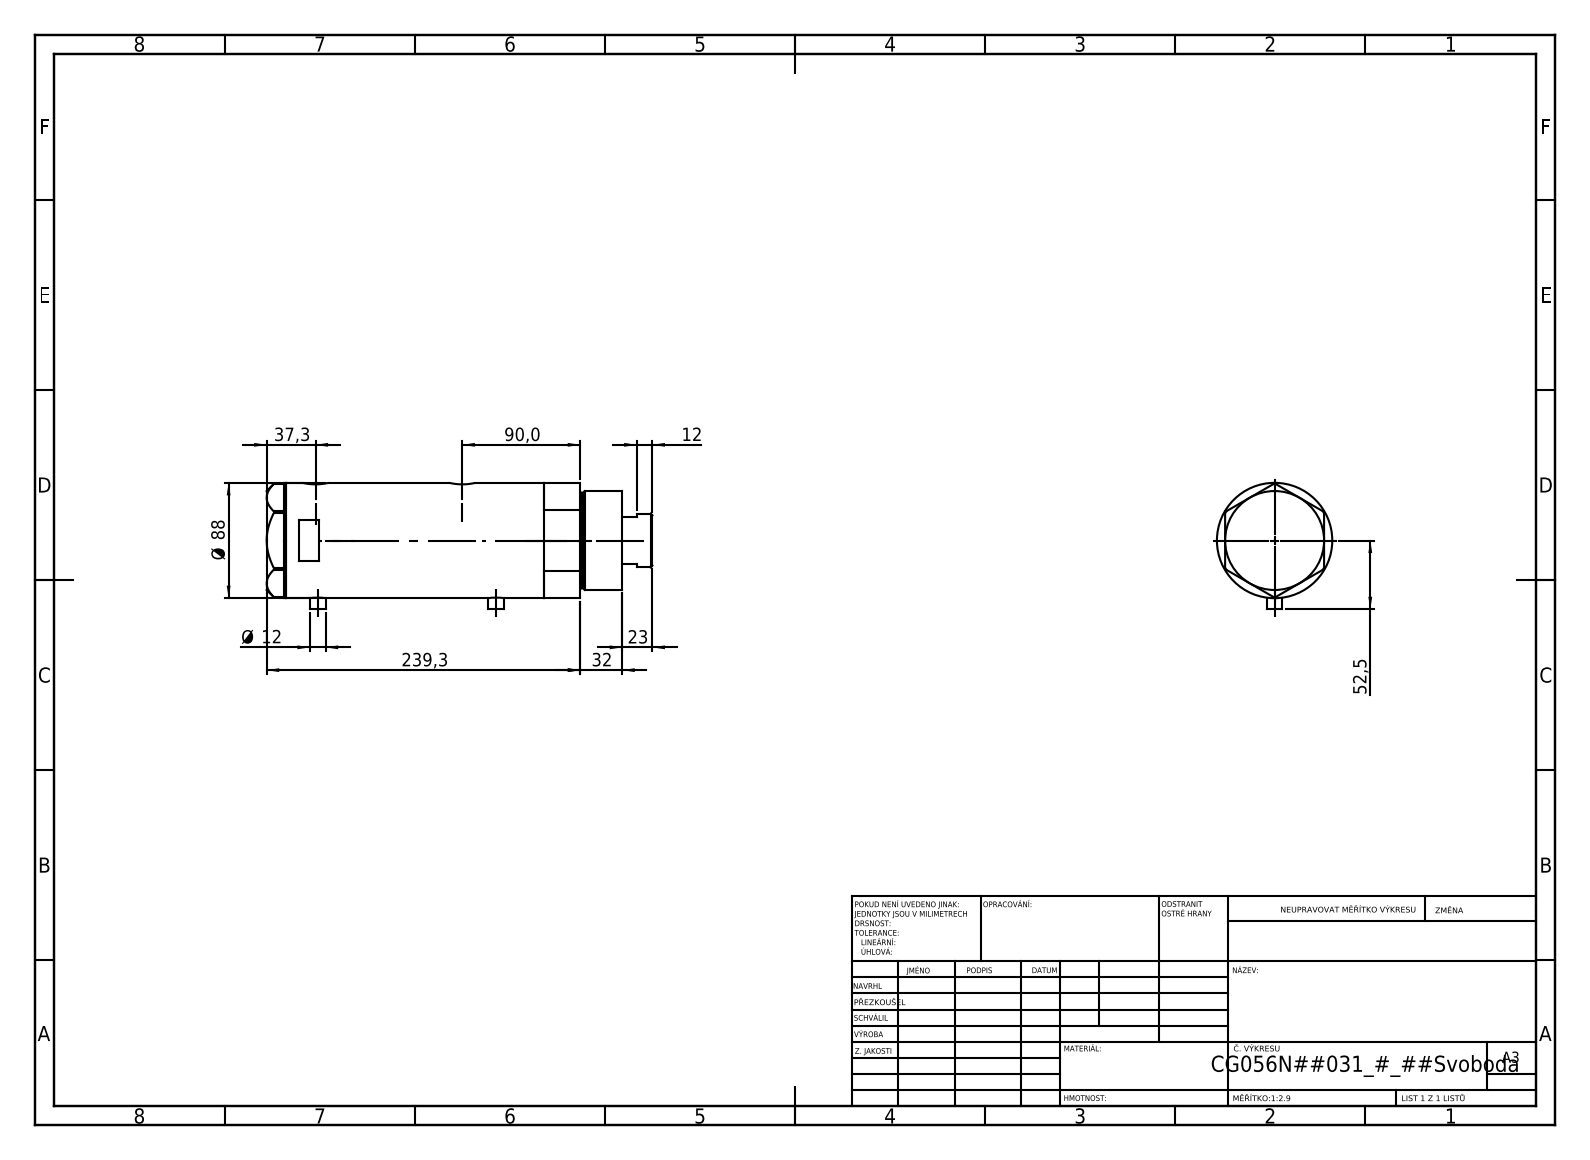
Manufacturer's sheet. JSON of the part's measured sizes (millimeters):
{"part_name": "V270CG_BACK; V270CG_VC; V270CG_MIDDLE; V270CG_FRONT", "step_written_by": "SolidWorks 2019 (CONFIG_CONTROL_DESIGN)", "units": "millimeters", "bodies": {"solids": 4, "faces": 126, "planar": 53, "cylindrical": 53, "other": 20}, "overall_size": [294.3, 96.5, 88], "volume_mm3": 1554000, "surface_area_mm2": 222743, "round_holes": [[5, 2], [12.5, 2], [13.16, 2], [20, 2], [14.5, 1], [42, 1], [43.5, 1], [56, 1], [60, 1], [80, 1]], "round_bosses_or_shafts": [[12, 2], [88, 1], [75, 1], [73, 1], [41, 1]], "face_to_face_distances": [134.4, 26, 108.4, 15, 41, 149.4, 256.3, 271.3, 230.3, 121.9], "hole_center_spacings": [1.7, 25.8, 110.3, 112, 136.1, 137.8]}
